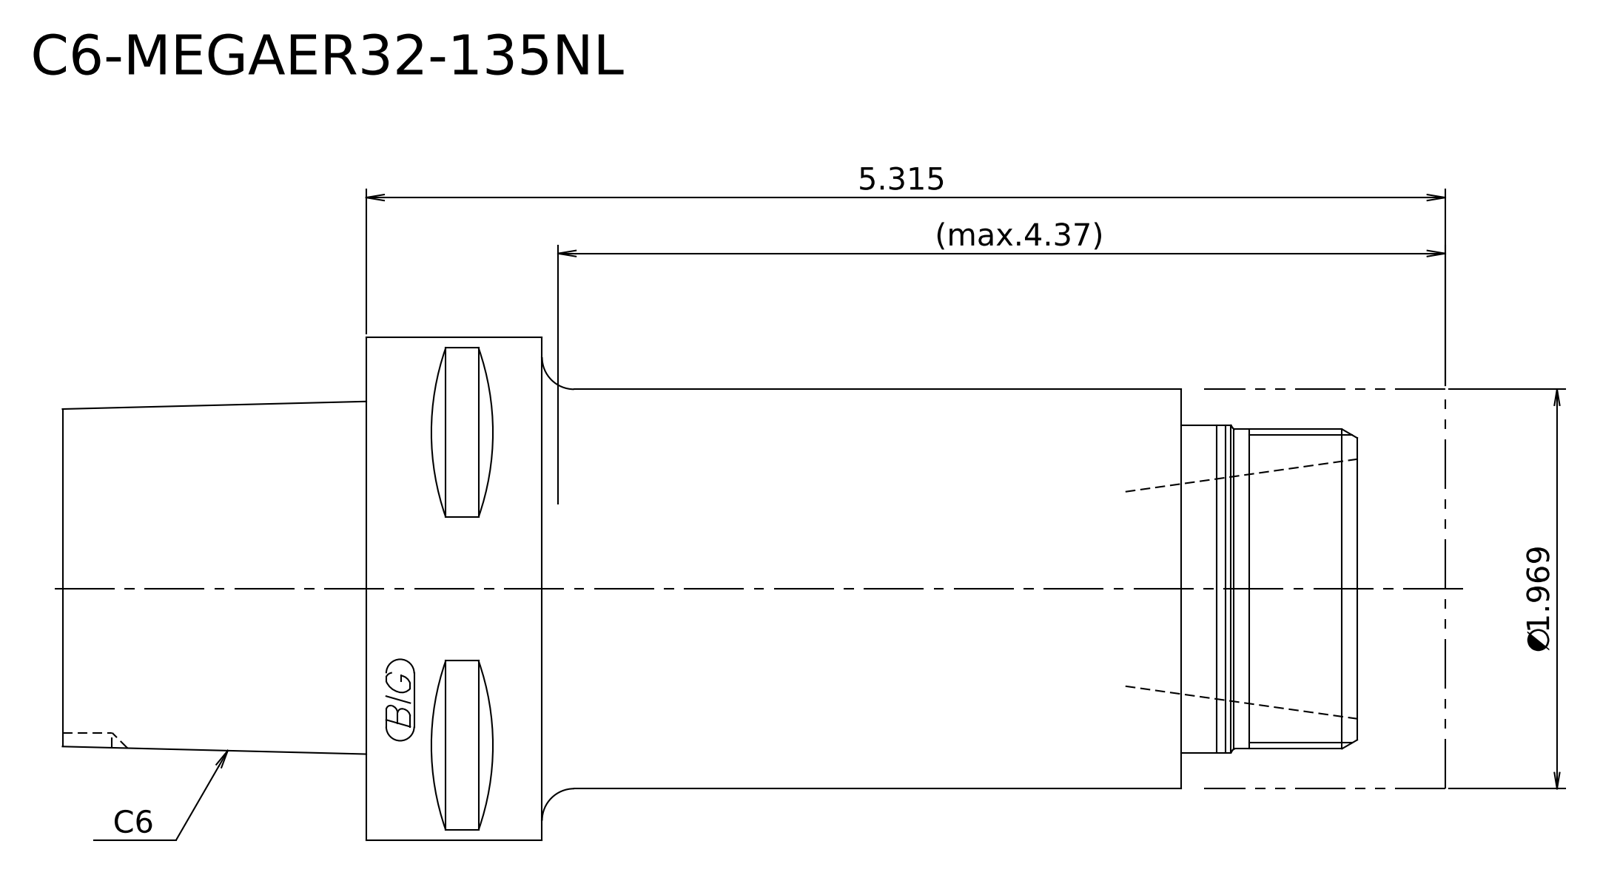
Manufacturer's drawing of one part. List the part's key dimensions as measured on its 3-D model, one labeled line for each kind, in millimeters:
STEP written by: Kubotek KeyCreator 2011 V10.0.2 (22737) (automotive_design)
Units: millimetres
Bodies: 2 solids, 18 faces (7 planar, 5 cylindrical, 6 other)
Overall size (bounding box): 173 × 63 × 63
Volume: 368 990 mm³ · Surface area: 39 161 mm²
Round bosses / shafts (diameter × count): ⌀63 ×1, ⌀50 ×1, ⌀41 ×1, ⌀40 ×1
Main face-to-face distances: 30.2, 135, 104.8, 173, 142.8, 38, 11, 19.2, 124, 162
